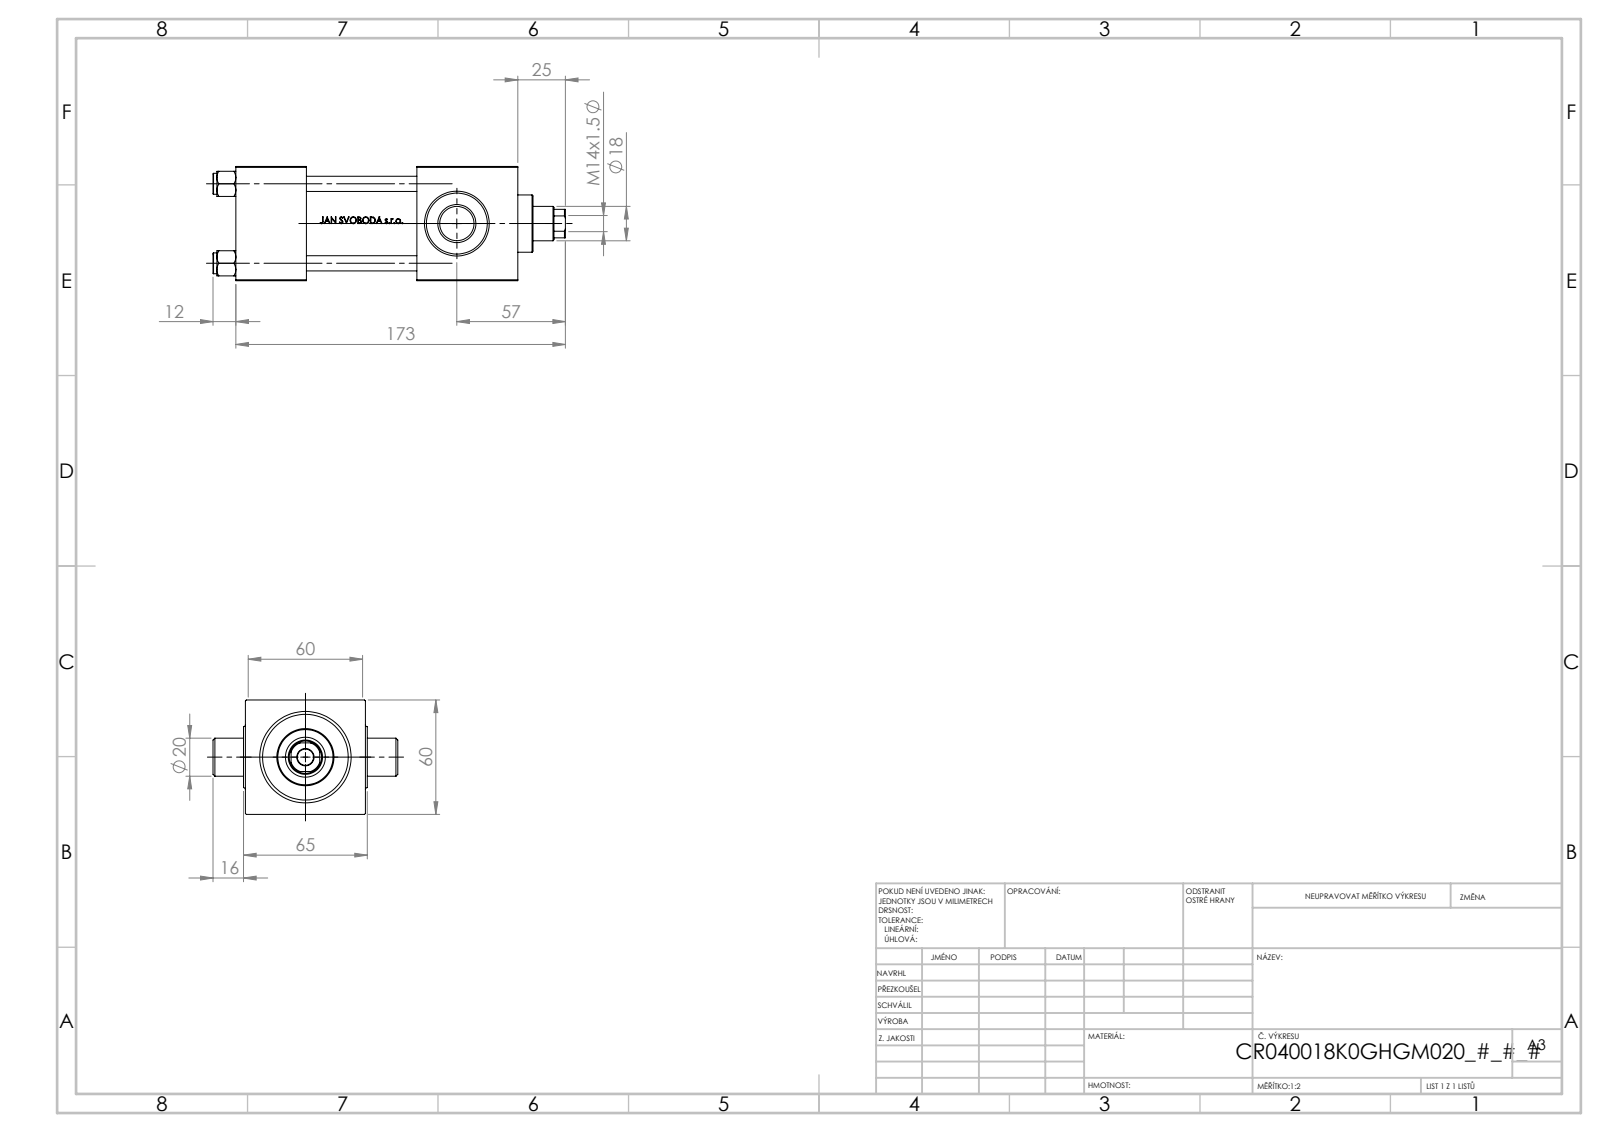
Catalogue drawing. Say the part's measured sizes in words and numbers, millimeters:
The part is named "V215CR_VCP_K; V215_VC_A; NUT_M5_K; V215CR_K_TYCINKA (+1 more)". Its 3-D file was written by "SolidWorks 2019 (CONFIG_CONTROL_DESIGN)". It is 11 solids with 1059 faces: 427 planar, 110 cylindrical and 522 other. Overall it measures 185 by 97 by 60 millimeters. Its volume is 431 735 cubic millimeters and its surface area 103 579 square millimeters. Round holes: 4 of diameter 8, 1 of diameter 7, 1 of diameter 8.5, 1 of diameter 18, 1 of diameter 21, 1 of diameter 31, 1 of diameter 40, 1 of diameter 45. Round bosses or shafts: 4 of diameter 11, 1 of diameter 46, 1 of diameter 30, 1 of diameter 20. Partial cylindrical surfaces (rounded edges, fillets, slot ends): 1 of radius 8.5. The main face-to-face distances are 60, 1.5, 61.5, 37, 148, 111, 95, 58, 53, 63. The hole center spacings are 29.49, 41.7, 58.97.
